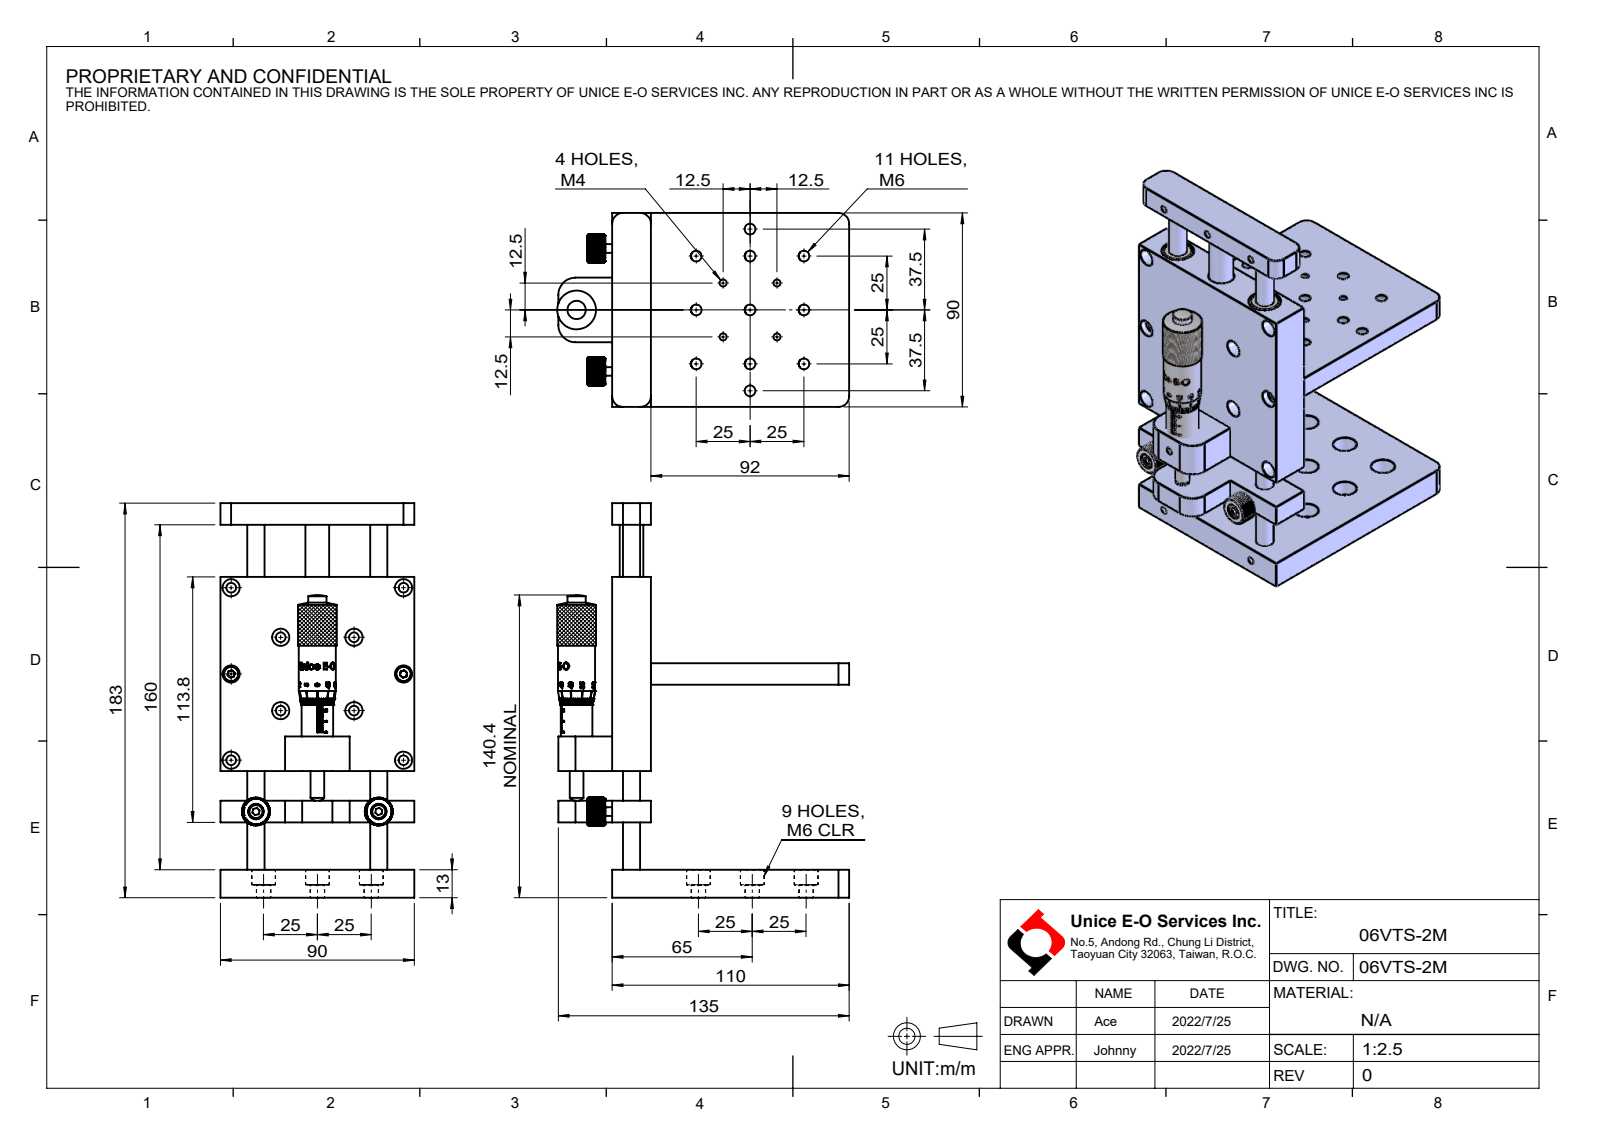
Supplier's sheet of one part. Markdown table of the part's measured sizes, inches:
| quantity | value |
| --- | --- |
| part name | 06VTS-2M |
| STEP written by | SolidWorks 2021 (CONFIG_CONTROL_DESIGN) |
| units | inches |
| bodies | 0 solids, 767 faces (321 planar, 297 cylindrical, 149 other) |
| overall size | 7.205 × 5.335 × 3.543 |
| round holes (diameter × count) | 0.197 × 23, 0.315 × 12, 0.13 × 10, 0.26 × 9, 0.433 × 9, 0.177 × 8, 0.283 × 2, 0.591 × 2, 0.394 × 1, 0.472 × 1 |
| round bosses / shafts (diameter × count) | 0.315 × 2, 0.157 × 2, 0.709 × 1, 0.677 × 1, 0.575 × 1, 0.433 × 1, 0.335 × 1, 0.25 × 1 |
| partial cylindrical surfaces (radius × count) | 0.197 × 6, 0.256 × 2, 0.315 × 2, 0.337 × 1 |
| main face-to-face distances | 0.394, 0.709, 0.512, 4.209, 3.698, 3.816, 3.304, 3.543, 2.438, 1.575 |
| hole center spacings | 0.984, 1.556, 2.244, 1.392, 0.696, 0.906, 2.201, 2.42 |
